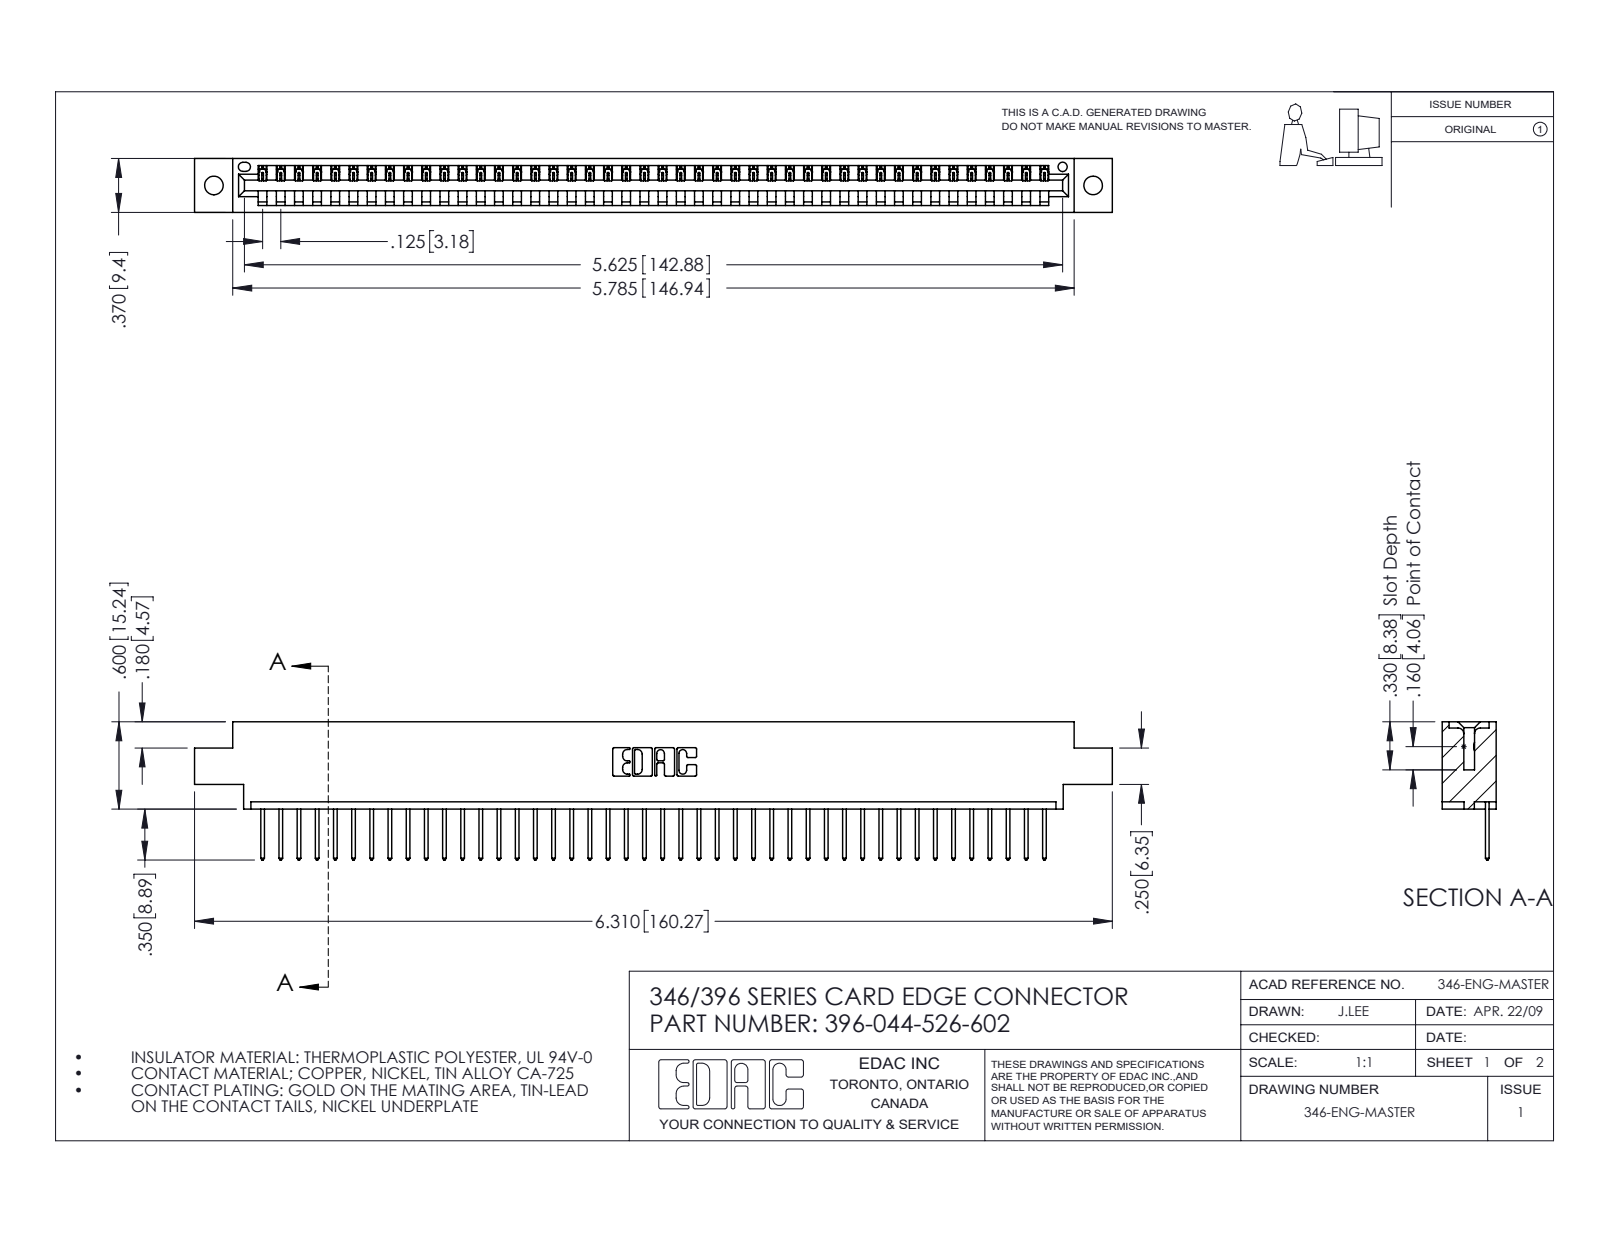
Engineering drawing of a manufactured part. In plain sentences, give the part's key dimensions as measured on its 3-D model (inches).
The part is named "345-292-001_345-293-126; 346 Part_0.170 Offset - 0.128 Dia; 396-044-526-602". Its 3-D file was written by "SolidWorks 2016 (CONFIG_CONTROL_DESIGN)". It is 45 solids with 2678 faces: 1840 planar, 838 cylindrical and 0 other. Overall it measures 6.31 by 0.95 by 0.37 inches. Its volume is 0.923 cubic inches and its surface area 29.1 square inches. Round holes: 2 of diameter 0.128, 1 of diameter 0.064. Partial cylindrical surfaces (rounded edges, fillets, slot ends): 88 of radius 0.006, 88 of radius 0.01, 22 of radius 0.01, 6 of radius 0.007, 6 of radius 0.031, 3 of radius 0.026, 2 of radius 0.031, 2 of radius 0.04. The main face-to-face distances are 0.048, 0.322, 0.37, 0.25, 0.072, 0.298, 0.025, 0.148, 0.222, 0.1. The hole center spacings are 0.246, 5.836, 6.045.
